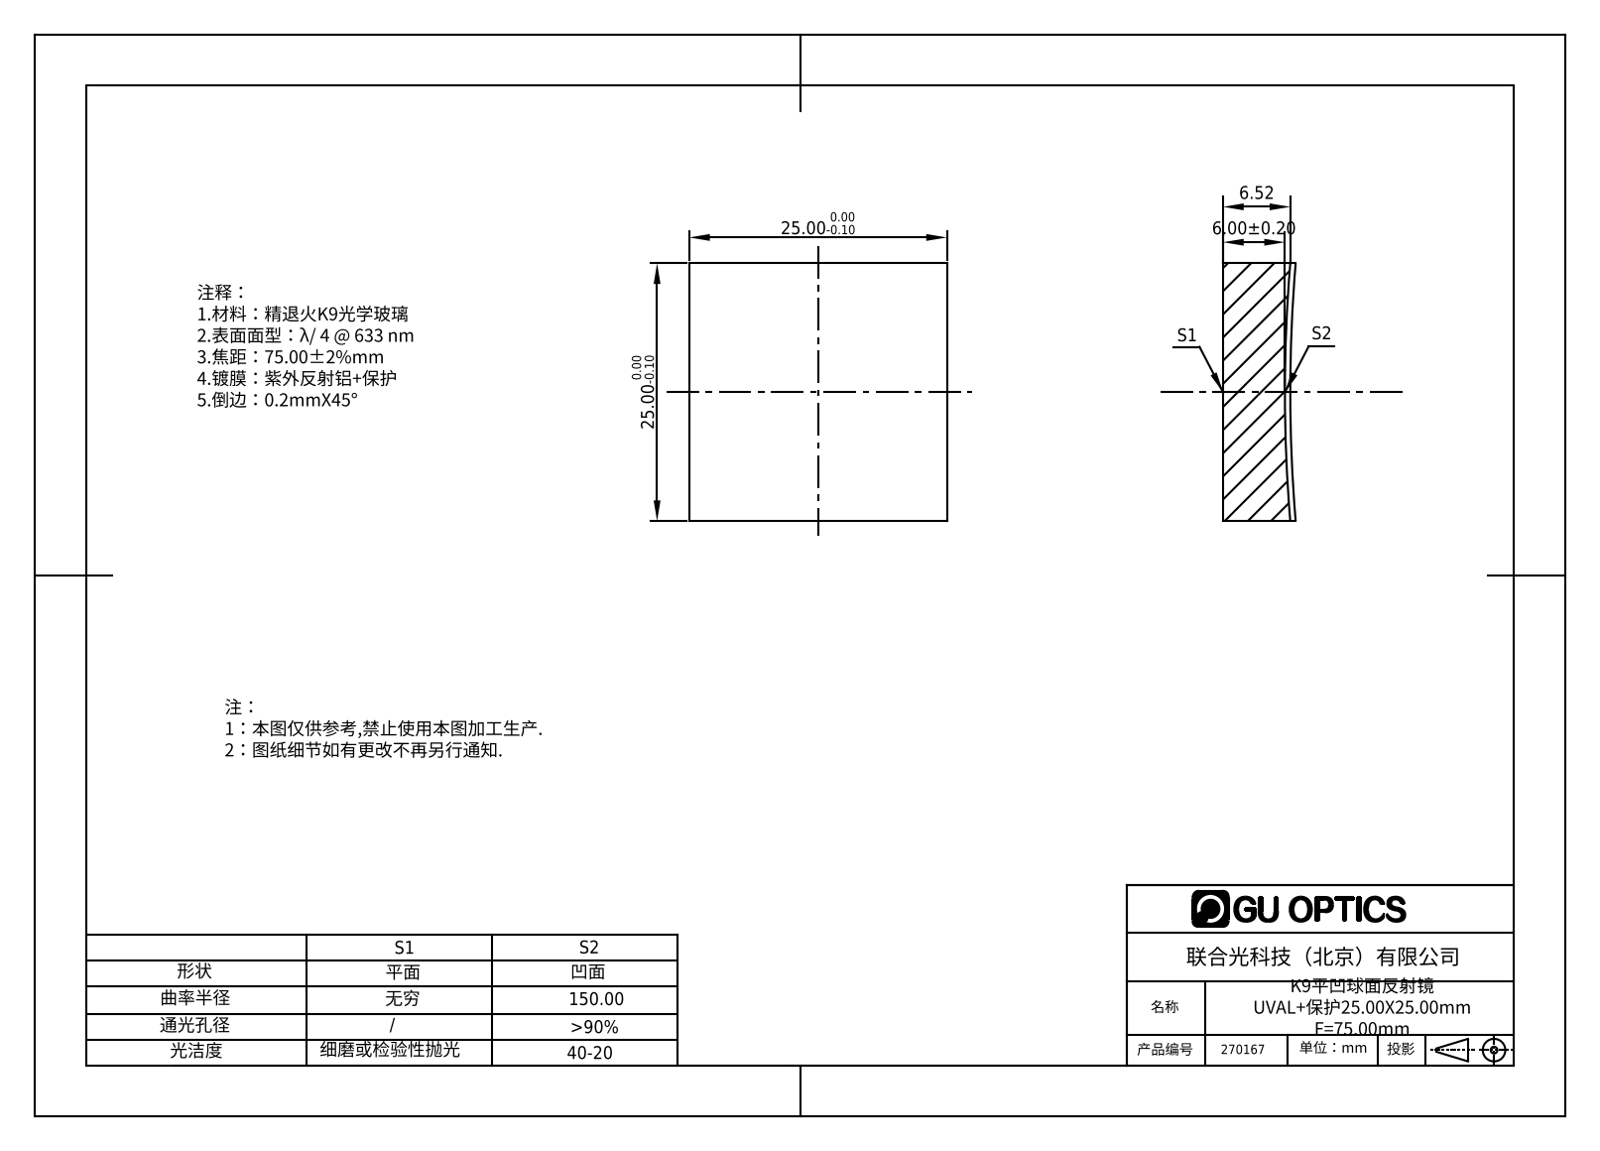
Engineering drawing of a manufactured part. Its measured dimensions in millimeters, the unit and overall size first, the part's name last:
Units: millimetres
Overall size (bounding box): 25 × 25 × 7.04
Main face-to-face distances: 25
Volume: 3 967 mm³ · Surface area: 1 921 mm²
Bodies: 1 solid, 7 faces (5 planar, 0 cylindrical, 2 other)
Part name (STEP PRODUCT): 270037
STEP written by: SolidWorks 2019 (AUTOMOTIVE_DESIGN)
